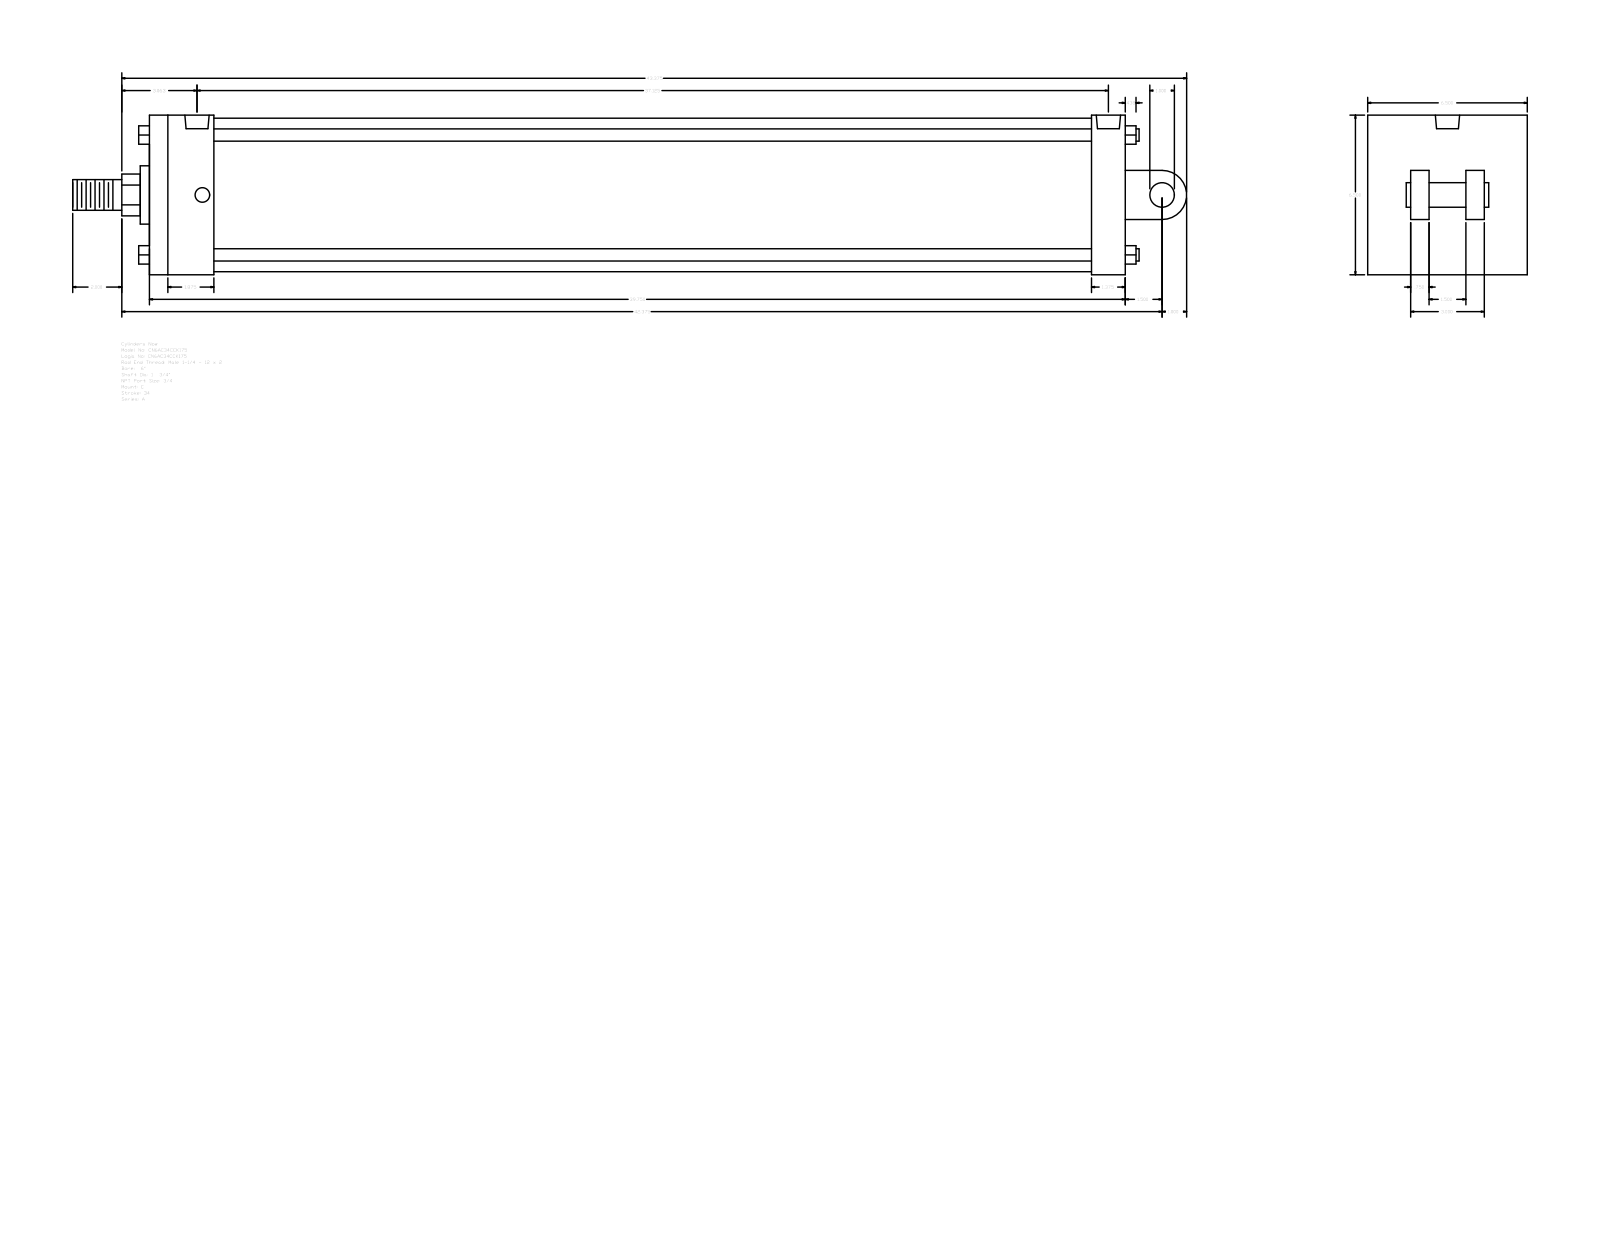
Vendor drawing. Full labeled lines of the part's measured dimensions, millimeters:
Part name (STEP PRODUCT): A_C__0600_1.75
STEP written by: GSSL Pune (CONFIG_CONTROL_DESIGN)
Units: millimetres
Bodies: 0 solids, 135 faces (102 planar, 33 cylindrical, 0 other)
Overall size (bounding box): 1152.53 × 165.1 × 165.1
Round holes (diameter × count): ⌀15.08 ×4, ⌀25.12 ×2
Round bosses / shafts (diameter × count): ⌀12.7 ×4, ⌀158.75 ×1, ⌀60.33 ×1, ⌀44.45 ×1, ⌀31.75 ×1, ⌀25.4 ×1
Partial cylindrical surfaces — rounded edges, fillets, slot ends (radius × count): R21.63 ×1, R25.4 ×1
Main face-to-face distances: 165.1, 1009.65, 19.05, 57.15, 66.68, 942.97, 974.73, 908.05, 34.92, 63.5
Hole centre spacings: 5.56, 931.85, 937.41, 942.97
